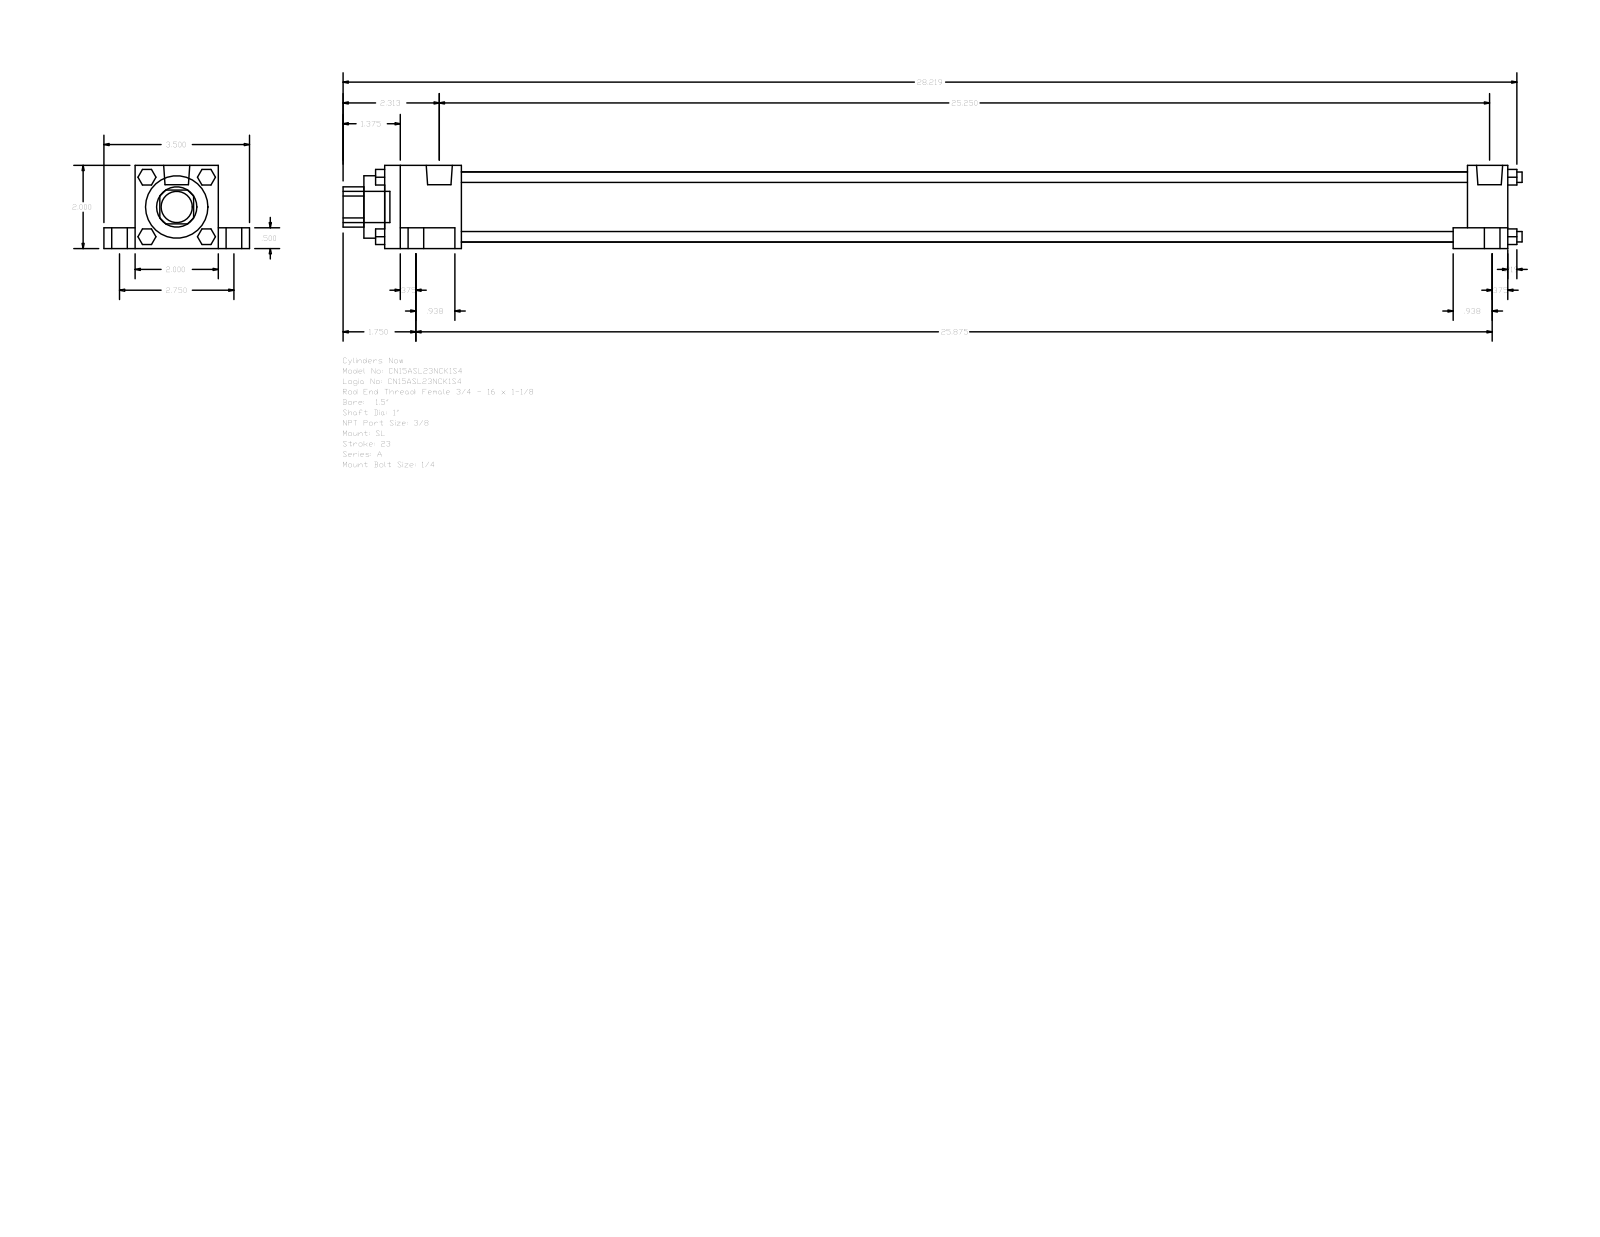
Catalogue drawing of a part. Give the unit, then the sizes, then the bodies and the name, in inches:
Units: inches
Overall size (bounding box): 28.344 × 3.5 × 2
Round holes (diameter × count): ⌀1 ×1, ⌀1.5 ×1, ⌀1.69 ×1
Round bosses / shafts (diameter × count): ⌀0.625 ×4, ⌀0.375 ×4, ⌀0.25 ×4, ⌀0.219 ×4, ⌀0.627 ×2, ⌀0.75 ×1
Partial cylindrical surfaces — rounded edges, fillets, slot ends (radius × count): R0.484 ×1
Main face-to-face distances: 2, 0.5, 1.5, 0.75, 2.75, 0.375, 27, 1.313, 26.031, 0.969
Bodies: 0 solids, 148 faces (112 planar, 36 cylindrical, 0 other)
Part name (STEP PRODUCT): A_SL__0150_1
STEP written by: GSSL Pune (CONFIG_CONTROL_DESIGN)
